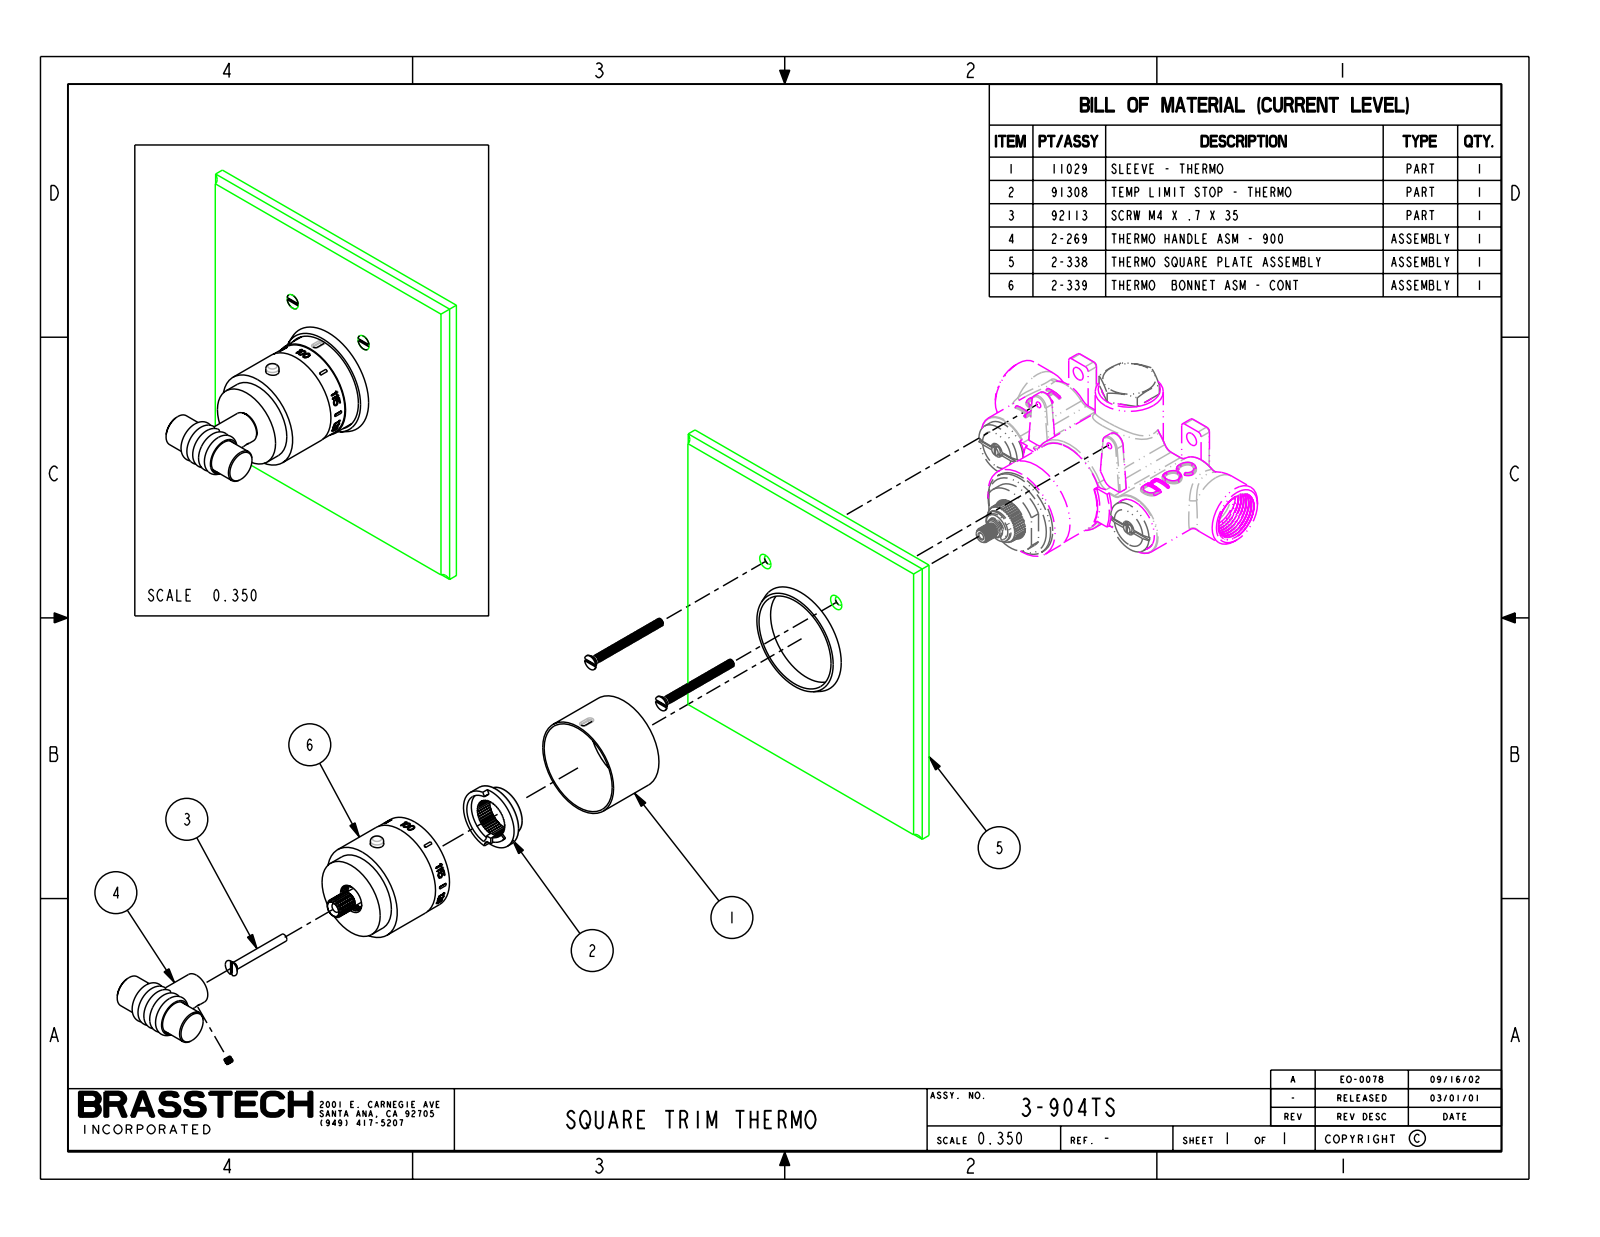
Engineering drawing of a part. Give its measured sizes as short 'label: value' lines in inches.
name: 11029_AF0; 11035; 11032; 91307 (+8 more)
written by: PRO/ENGINEER BY PARAMETRIC TECHNOLOGY CORPORATION, 2013150 (CONFIG_CONTROL_DESIGN)
unit: in
bodies: 22 solids, 1602 faces (784 planar, 477 cylindrical, 341 other)
size: 6.5 × 6.5 × 4.485
volume: 6.028 in³; area: 236.3 in²
holes: 2× ⌀0.13, 1× ⌀0.028, 1× ⌀0.118, 1× ⌀0.188, 1× ⌀0.206, 1× ⌀0.265, 1× ⌀0.27, 1× ⌀0.272, 1× ⌀0.46, 1× ⌀0.508, 1× ⌀0.65, 1× ⌀0.68
bosses: 4× ⌀0.164, 2× ⌀0.31, 2× ⌀0.157, 2× ⌀0.13, 1× ⌀2.14, 1× ⌀1.97, 1× ⌀1.94, 1× ⌀1.929
rounds: 4× R0.125, 4× R0.175, 2× R0.075, 2× R0.086, 2× R0.188, 1× R0.02, 1× R0.055, 1× R0.109
face distances: 0.05, 6.5, 6.45, 2.317, 2.267, 6.4, 2.006, 1.956, 0.312, 0.263
hole spacings: 0.567, 0.931
